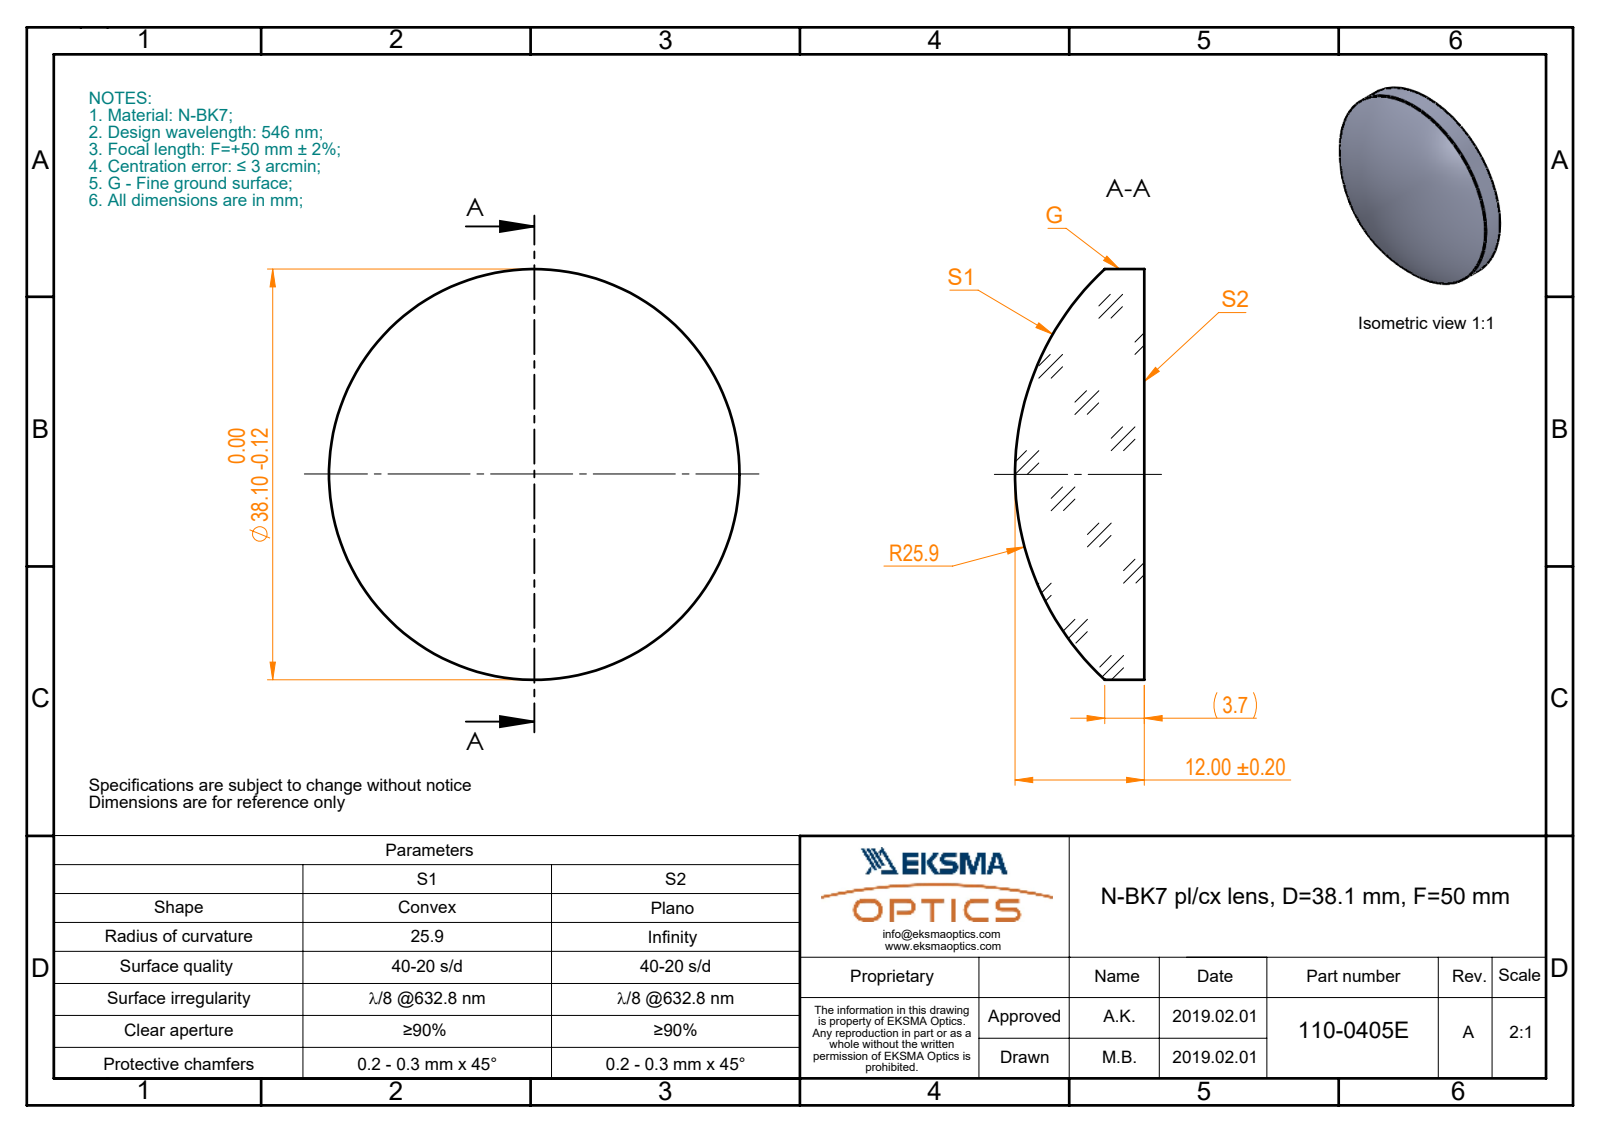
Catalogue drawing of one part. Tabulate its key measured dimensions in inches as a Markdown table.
| quantity | value |
| --- | --- |
| part name | 110-0405E BK7 pl-cx 38.1 F50 |
| STEP written by | SolidWorks 2017 (CONFIG_CONTROL_DESIGN) |
| units | inches |
| bodies | 1 solid, 5 faces (1 planar, 2 cylindrical, 2 other) |
| overall size | 1.5 × 1.5 × 0.472 |
| volume | 0.563 in³ |
| surface area | 4.552 in² |
| round bosses / shafts (diameter × count) | 1.5 × 1 |
